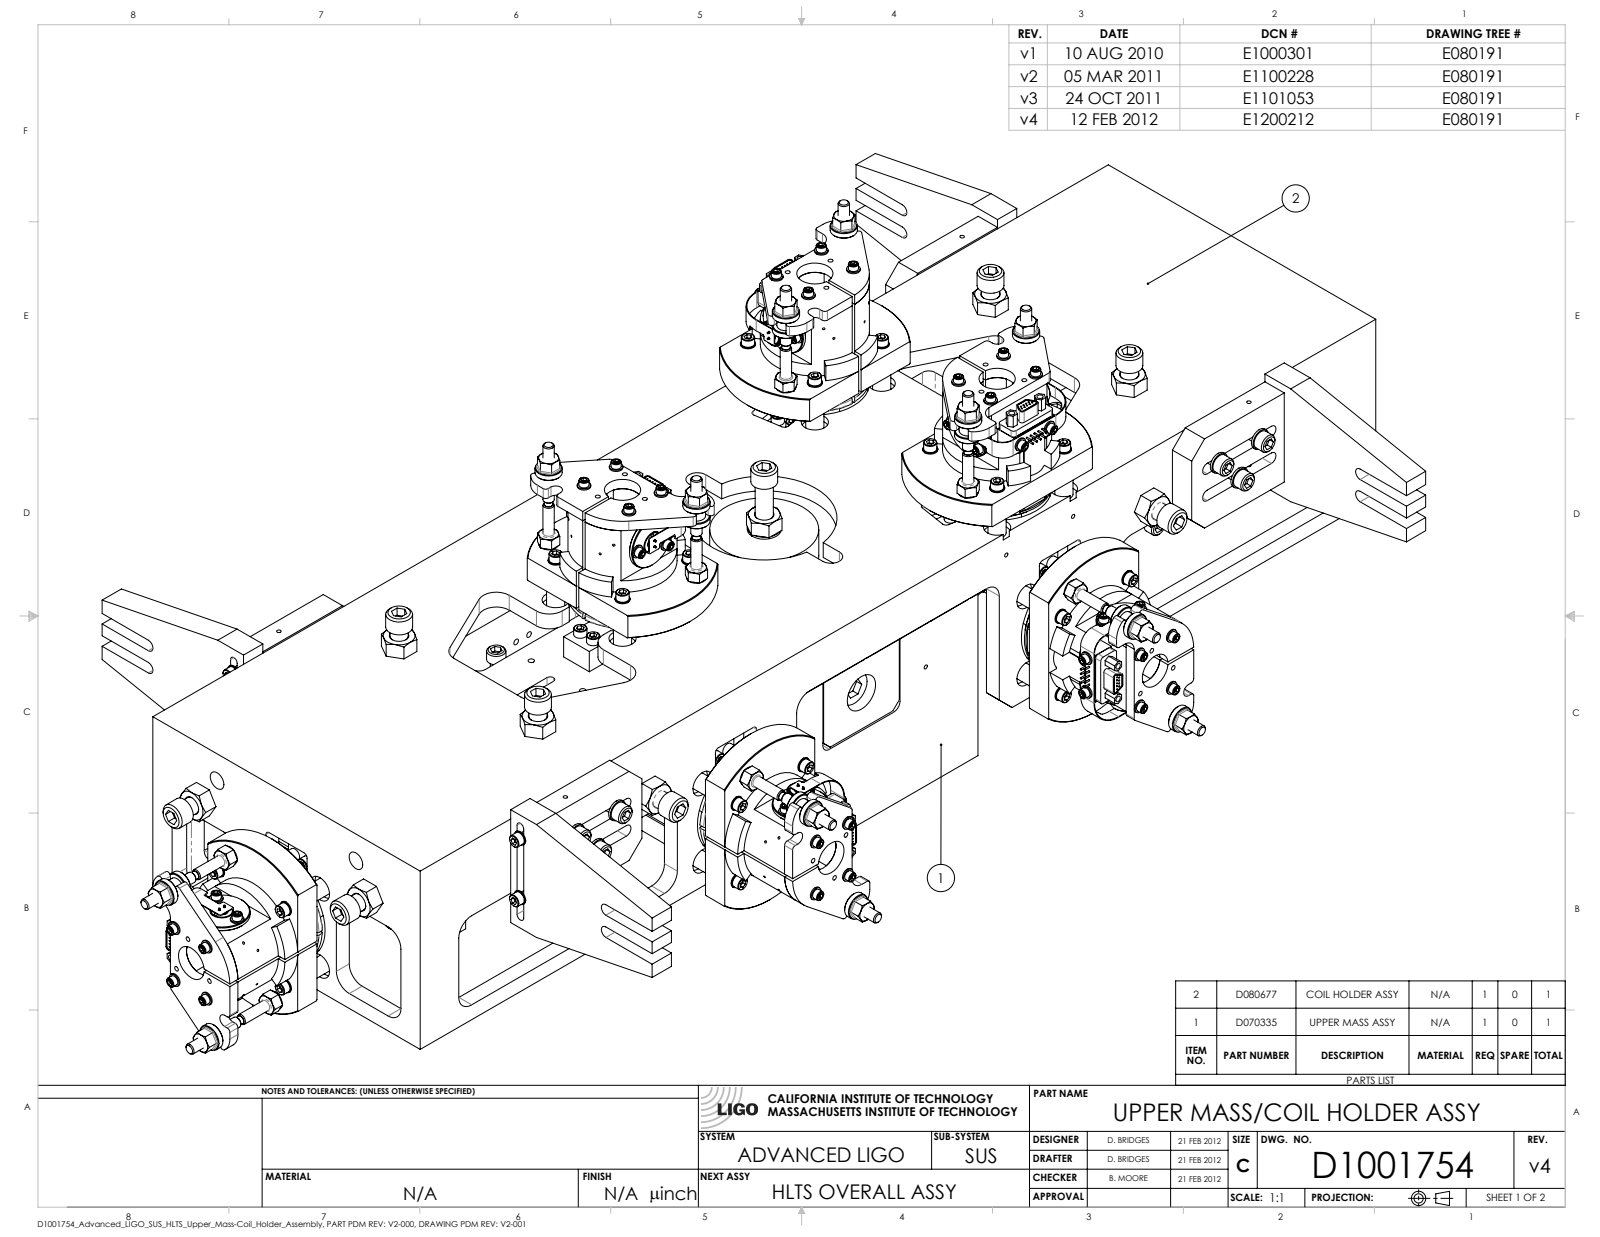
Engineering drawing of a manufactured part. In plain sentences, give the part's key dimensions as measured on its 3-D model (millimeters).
The part is named "D1001754-v4; D080677_Advanced_LIGO_SUS_HLTS_Coil_Holder_Assembly; Rounded_SHCS_RSHCS 0.25-20 X 1; Helicoil_0.25-20 X 0.25 LONG (+8 more)". Its 3-D file was written by "SolidWorks 2012 (CONFIG_CONTROL_DESIGN)". It is 155 solids with 4216 faces: 1850 planar, 1611 cylindrical and 755 other. Overall it measures 563.1 by 261.1 by 187.7 millimeters. Its volume is 703 300 cubic millimeters and its surface area 360 300 square millimeters. Round holes: 35 of diameter 2.3, 18 of diameter 0.5, 14 of diameter 4.4, 12 of diameter 0.8, 12 of diameter 2.9, 12 of diameter 3.3, 12 of diameter 9.5, 12 of diameter 9.5, 11 of diameter 6.8, 8 of diameter 1.6, 8 of diameter 2.8, 8 of diameter 3. Round bosses or shafts: 25 of diameter 4.6, 23 of diameter 2.8, 18 of diameter 6.4, 18 of diameter 0.5, 17 of diameter 4.8, 17 of diameter 3.6, 12 of diameter 5.3, 9 of diameter 6.8. Partial cylindrical surfaces (rounded edges, fillets, slot ends): 32 of radius 6.4, 24 of radius 0.4, 24 of radius 1.3, 22 of radius 0.5, 10 of radius 1.6, 10 of radius 2.5, 10 of radius 3.2, 8 of radius 1. The main face-to-face distances are 6.4, 125.7, 132.1, 119.4, 69.9, 465.6, 76.2, 471.9, 459.2, 9.5. The hole center spacings are 33, 23.3, 18, 3, 16.5, 21.3, 25.6, 46.7.
